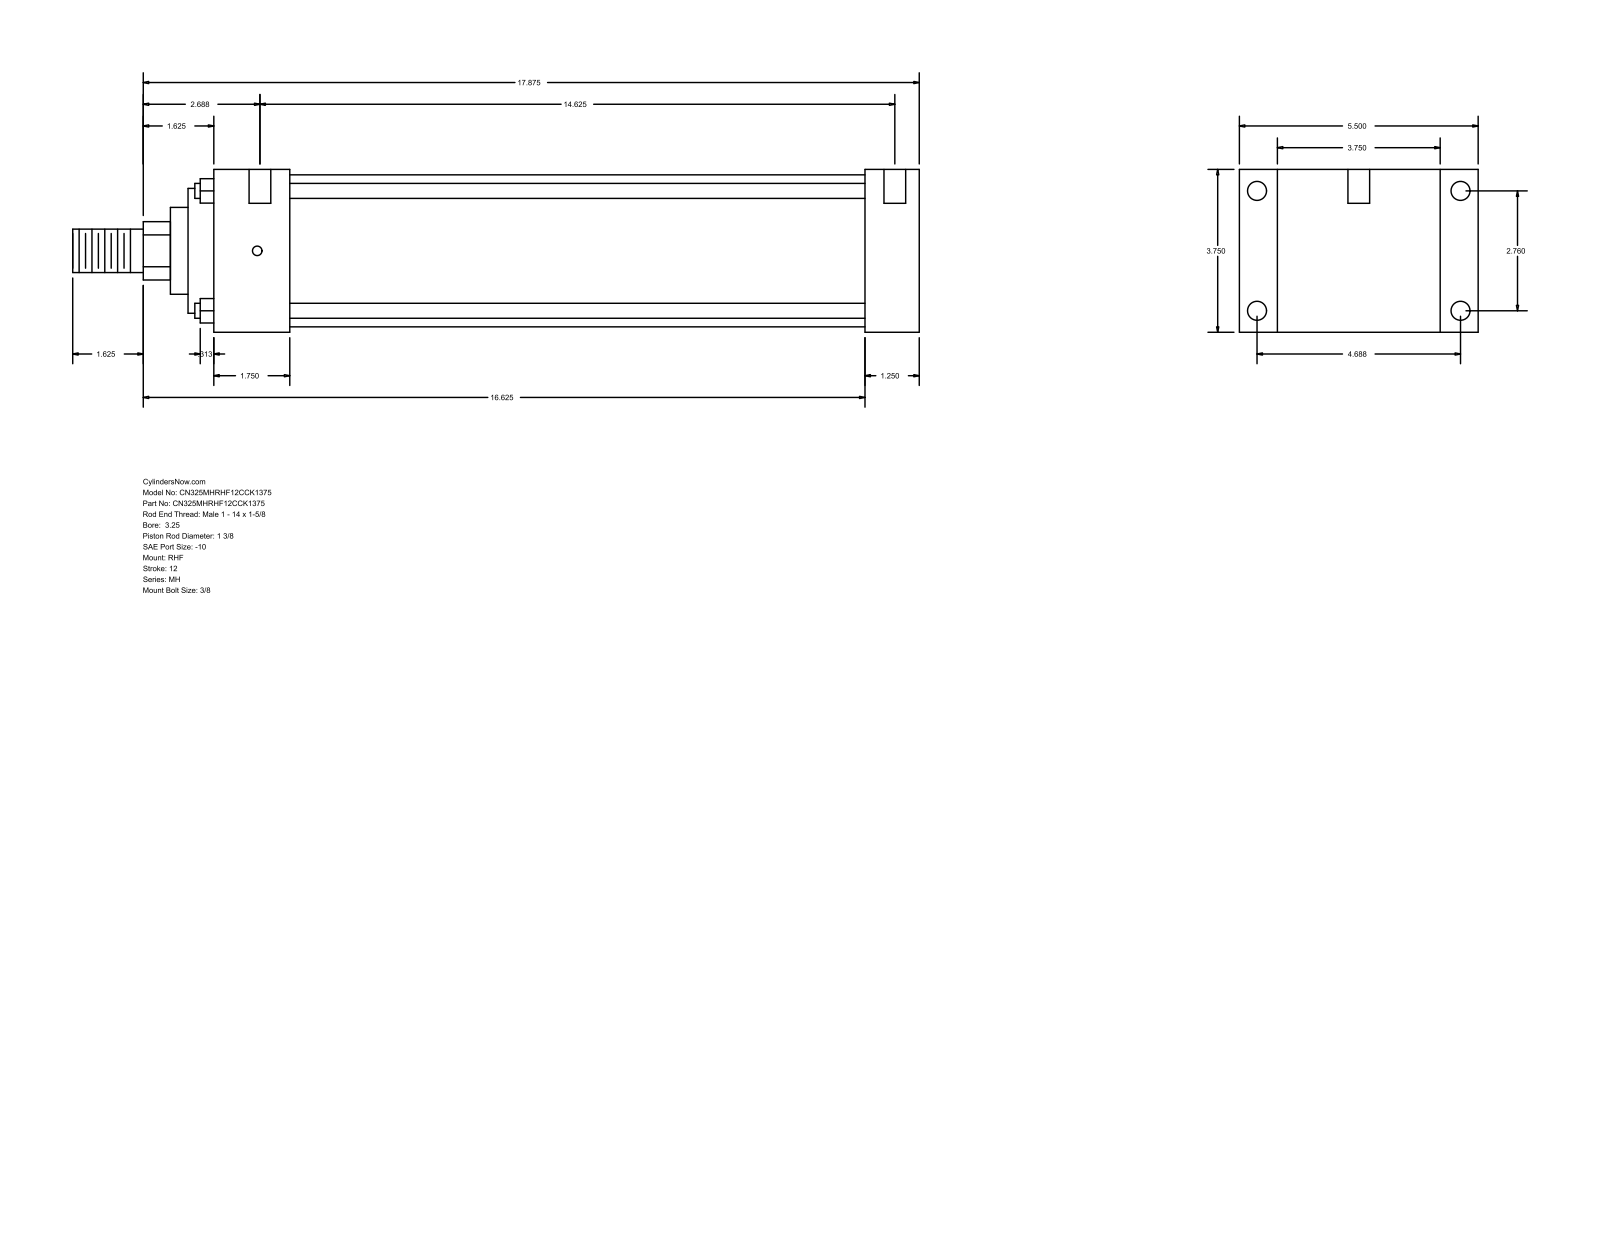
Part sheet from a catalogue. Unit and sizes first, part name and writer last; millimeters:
Units: millimetres
Overall size (bounding box): 495.3 × 139.7 × 95.25
Round holes (diameter × count): ⌀5.56 ×4, ⌀11.13 ×4, ⌀12.7 ×2
Round bosses / shafts (diameter × count): ⌀8.76 ×4, ⌀88.9 ×1, ⌀73.03 ×1, ⌀50.8 ×1, ⌀34.92 ×1, ⌀25.4 ×1
Partial cylindrical surfaces — rounded edges, fillets, slot ends (radius × count): R17.06 ×1
Main face-to-face distances: 95.24, 31.75, 22.23, 117.47, 381, 412.75, 139.7, 44.45, 336.55, 368.3
Hole centre spacings: 70.1, 119.06, 138.16, 377.83, 1.59, 4.76, 371.48, 373.07
Bodies: 0 solids, 90 faces (61 planar, 29 cylindrical, 0 other)
Part name (STEP PRODUCT): MH_RHF__0325_1.375
STEP written by: GSSL Pune (CONFIG_CONTROL_DESIGN)
